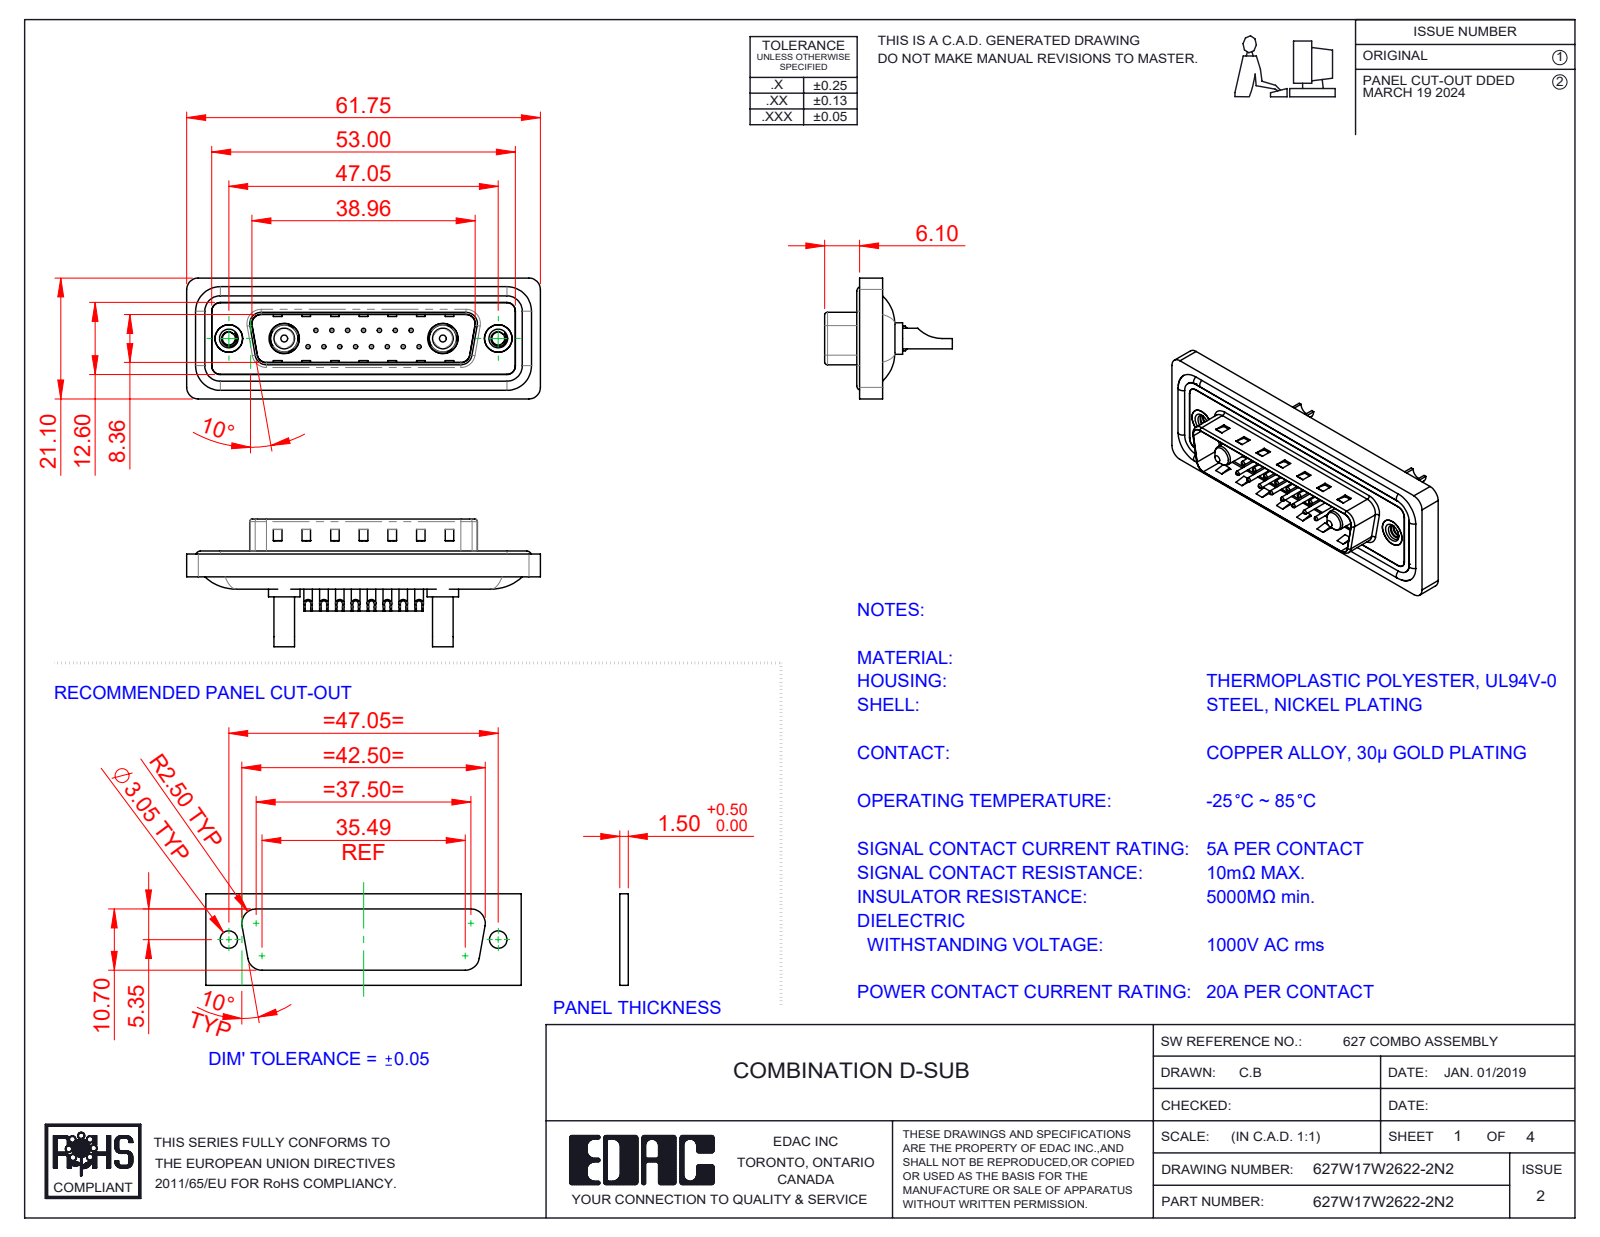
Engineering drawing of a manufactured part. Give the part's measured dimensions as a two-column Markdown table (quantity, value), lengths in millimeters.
| quantity | value |
| --- | --- |
| part name | 627Combo Waterproof Housing_25 Contacts; 627W17W2622-2N2; 627Combo Contact Row 2_22; Power Pin_20A SC (+5 more) |
| STEP written by | SolidWorks 2023 (CONFIG_CONTROL_DESIGN) |
| units | millimeters |
| bodies | 26 solids, 1130 faces (370 planar, 472 cylindrical, 288 other) |
| overall size | 61.75 × 22.3 × 21.1 |
| volume | 7 315 mm³ |
| surface area | 12 198 mm² |
| round holes (diameter × count) | 0.75 × 15, 1 × 15, 1.6 × 15, 2 × 15, 2.26 × 2, 2.7 × 2, 4 × 2, 4.8 × 2, 4.85 × 2, 5 × 2, 5.3 × 2 |
| round bosses / shafts (diameter × count) | 1.5 × 15, 1.6 × 4, 5.5 × 2, 5.2 × 2, 4.9 × 2, 4.75 × 2, 3.75 × 2, 3.6 × 2 |
| partial cylindrical surfaces (radius × count) | 1.5 × 22, 2 × 18, 0.5 × 8, 1.6 × 8, 1 × 6, 0.25 × 4, 0.6 × 4, 0.65 × 4 |
| main face-to-face distances | 0.4, 1.5, 1.1, 1.6, 0.5, 3.1, 2.9, 0.82, 9.58, 4.1 |
| hole center spacings | 3.16, 2.77, 5.54, 8.31, 5.04, 7.49, 11.08, 5.03 |
